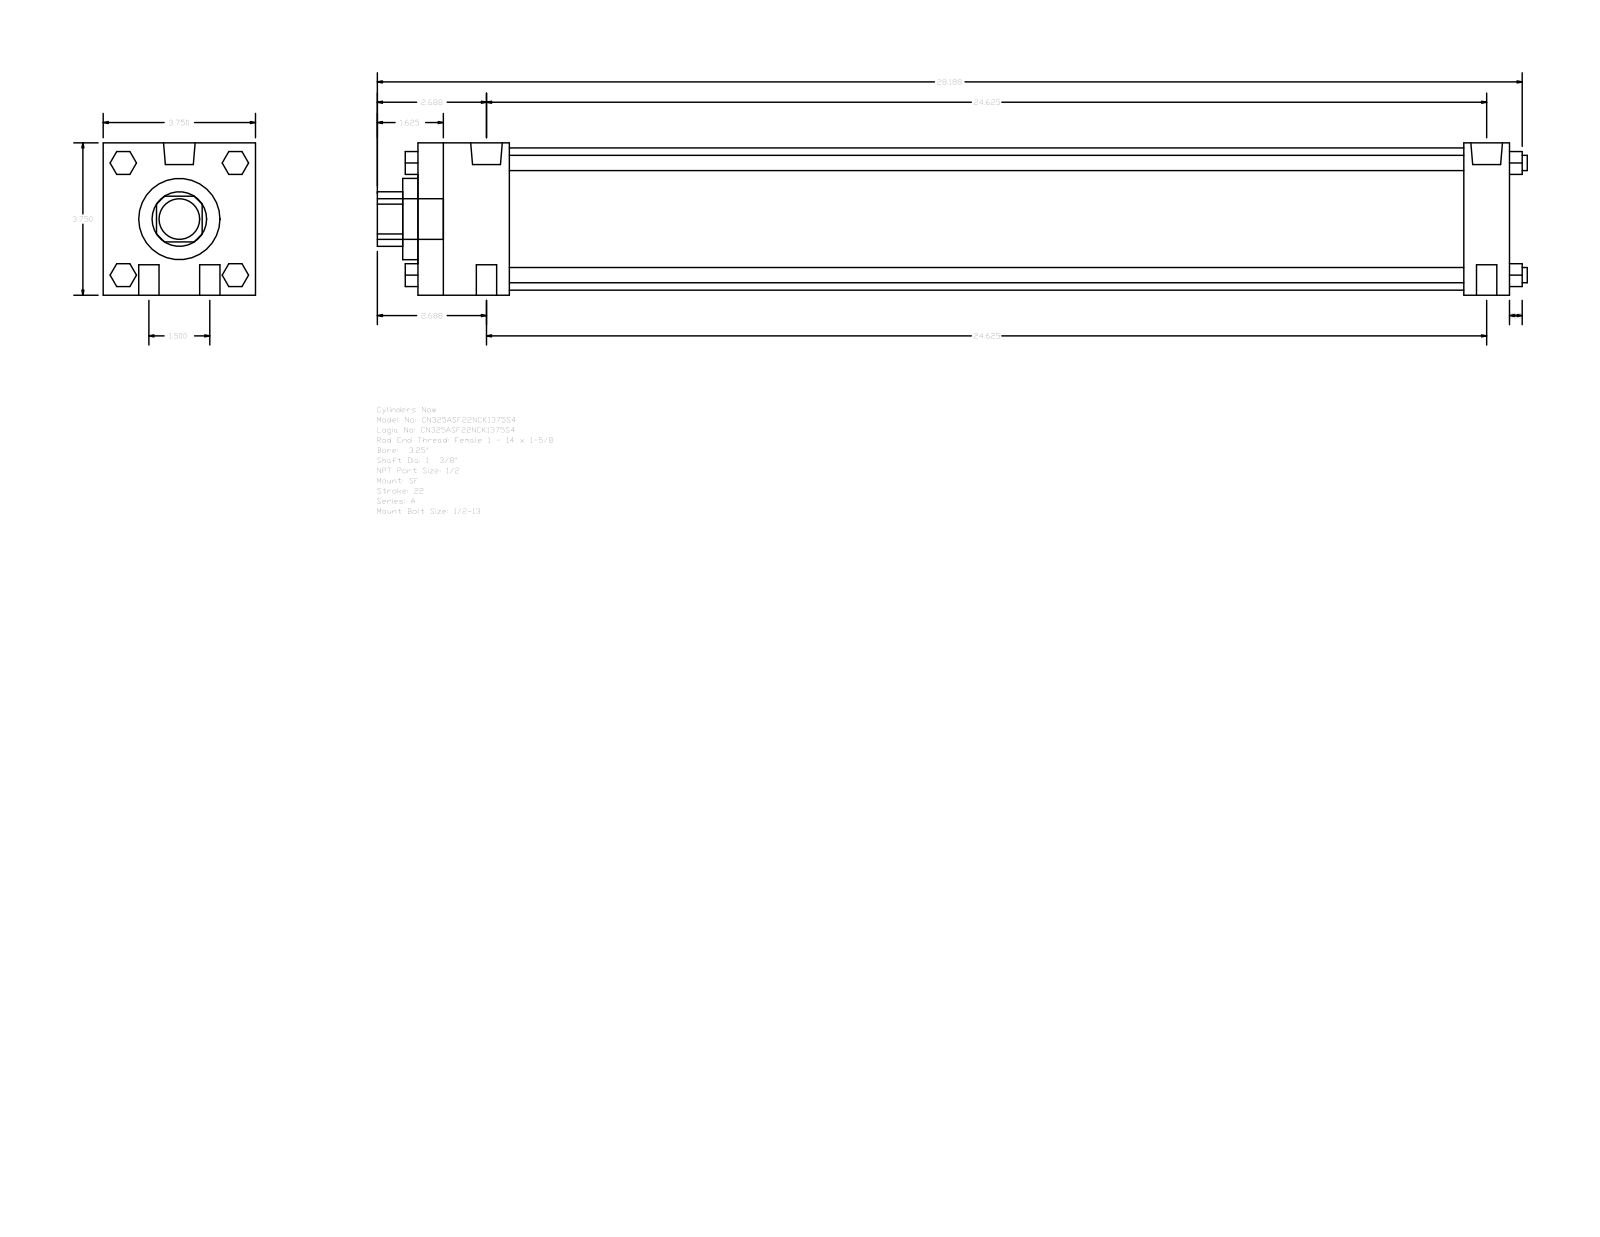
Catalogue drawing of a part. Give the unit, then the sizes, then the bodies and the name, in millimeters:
Units: millimetres
Overall size (bounding box): 719.14 × 95.25 × 95.25
Round holes (diameter × count): ⌀34.92 ×1, ⌀50.8 ×1, ⌀88.9 ×1
Round bosses / shafts (diameter × count): ⌀12.7 ×4, ⌀9.53 ×4, ⌀19.77 ×2, ⌀8.73 ×2, ⌀25.4 ×1
Partial cylindrical surfaces — rounded edges, fillets, slot ends (radius × count): R17.06 ×1
Main face-to-face distances: 95.24, 682.62, 28.57, 654.05, 57.15, 596.9, 625.47, 9.52, 66.67, 663.57
Bodies: 0 solids, 124 faces (94 planar, 30 cylindrical, 0 other)
Part name (STEP PRODUCT): A_SF__0325_1.375
STEP written by: GSSL Pune (CONFIG_CONTROL_DESIGN)
